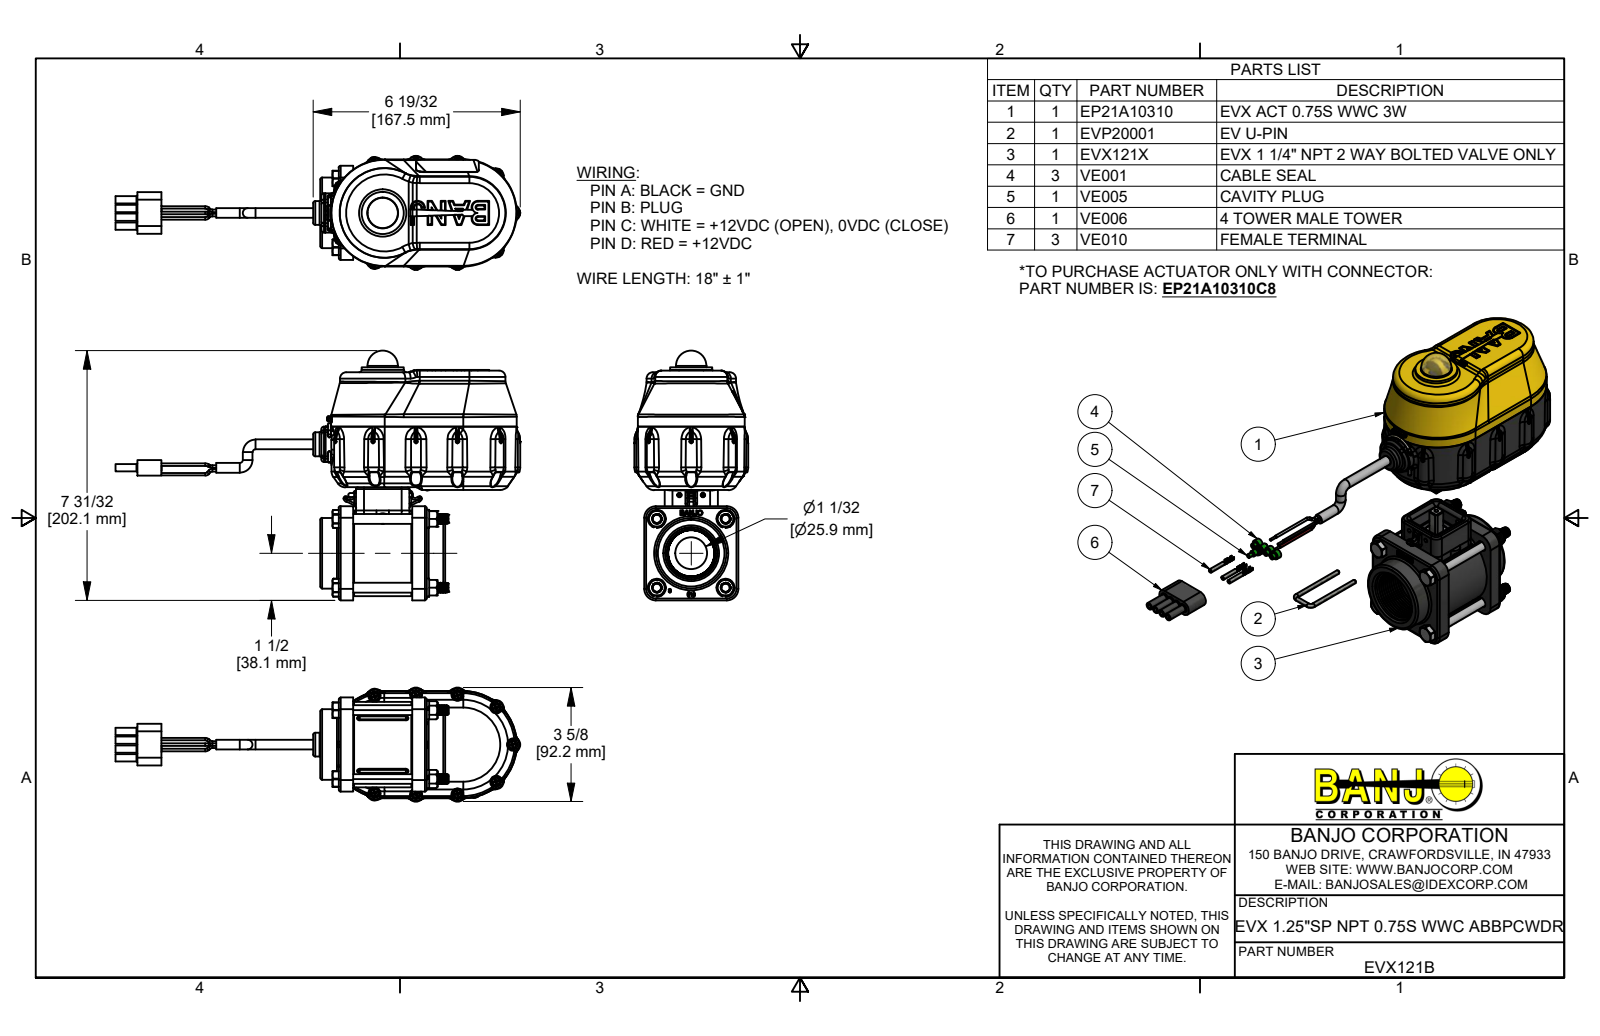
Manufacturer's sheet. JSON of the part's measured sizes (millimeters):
{"part_name": "EVX121B; EP21A10310; EP10310; IRF4905 (+8 more)", "step_written_by": "Autodesk Inventor 2019 (AUTOMOTIVE_DESIGN)", "units": "millimeters", "bodies": {"solids": 104, "faces": 11782, "planar": 3064, "cylindrical": 3503, "other": 5215}, "overall_size": [1258.6, 202.1, 92.2], "volume_mm3": 805900, "surface_area_mm2": 562800, "round_holes": [[2.4, 11], [3.8, 11], [2, 7], [2.7, 4], [3.2, 4], [3.4, 4], [3.5, 4], [3.6, 4], [3.8, 4], [3.8, 4], [4.3, 4], [6.2, 4]], "round_bosses_or_shafts": [[6.8, 60], [6.4, 17], [2, 15], [3.6, 11], [2.7, 11], [2.2, 11], [1.5, 6], [8, 5]], "partial_cylinders_radius": [[0.3, 180], [1, 145], [0.3, 84], [0.5, 72], [1.5, 58], [0.1, 53], [0.8, 38], [2, 28]], "face_to_face_distances": [2.5, 65.2, 5.4, 1.5, 3.8, 11.7, 59.6, 1.4, 3.2, 48.2], "hole_center_spacings": [22.1, 22.9, 26.6, 39.4, 42.2, 48, 55.7, 67.5]}
